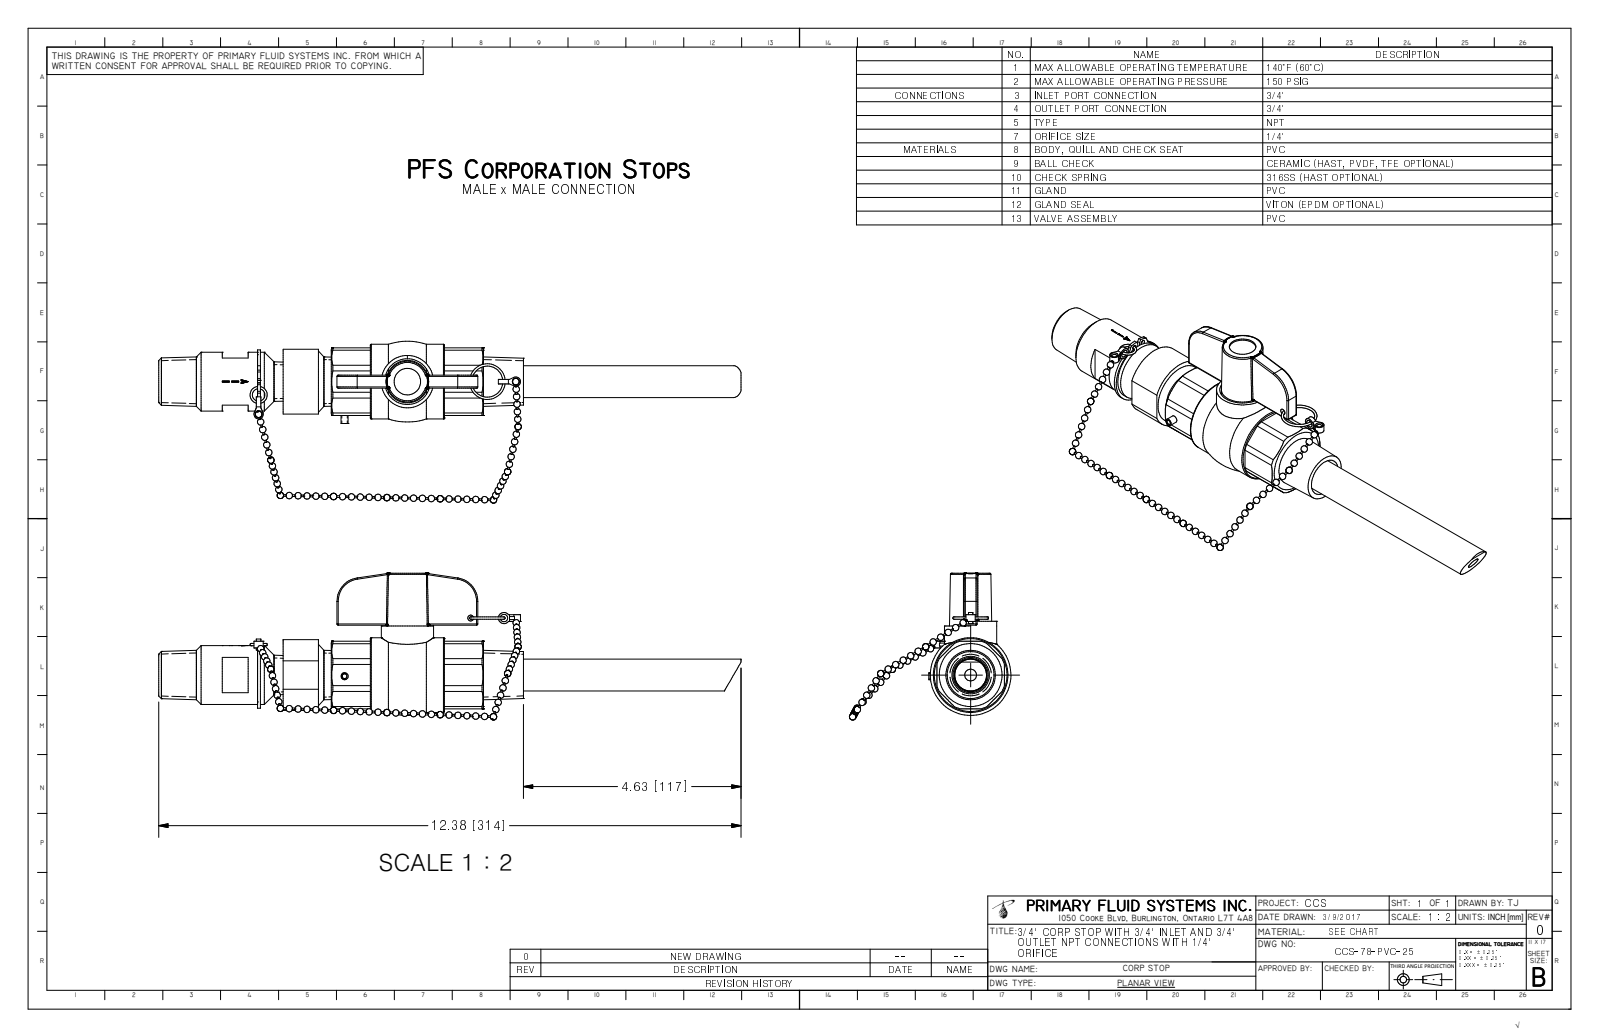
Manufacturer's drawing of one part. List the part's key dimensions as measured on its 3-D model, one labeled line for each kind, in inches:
Part name (STEP PRODUCT): CCS-78-PVC-25_R0
STEP written by: Autodesk Inventor 2009 (AUTOMOTIVE_DESIGN)
Units: inches
Bodies: 1 solid, 393 faces (114 planar, 59 cylindrical, 220 other)
Overall size (bounding box): 12.38 × 3.433 × 3.114
Volume: 13.55 in³ · Surface area: 74.22 in²
Round holes (diameter × count): ⌀0.098 ×1, ⌀0.15 ×1, ⌀0.25 ×1, ⌀0.469 ×1, ⌀0.56 ×1, ⌀0.563 ×1, ⌀0.97 ×1
Round bosses / shafts (diameter × count): ⌀1.585 ×1, ⌀1.343 ×1, ⌀1.25 ×1, ⌀1.14 ×1, ⌀1.11 ×1, ⌀0.9 ×1, ⌀0.675 ×1, ⌀0.558 ×1
Partial cylindrical surfaces — rounded edges, fillets, slot ends (radius × count): R0.025 ×12, R0.054 ×2, R0.197 ×2, R0.5 ×2, R0.451 ×1, R0.624 ×1, R0.75 ×1, R0.752 ×1
Main face-to-face distances: 1.435, 0.55, 0.03, 0.275, 0.825, 0.187, 1.187, 0.363, 0.637, 0.217
Hole centre spacings: 0.657
